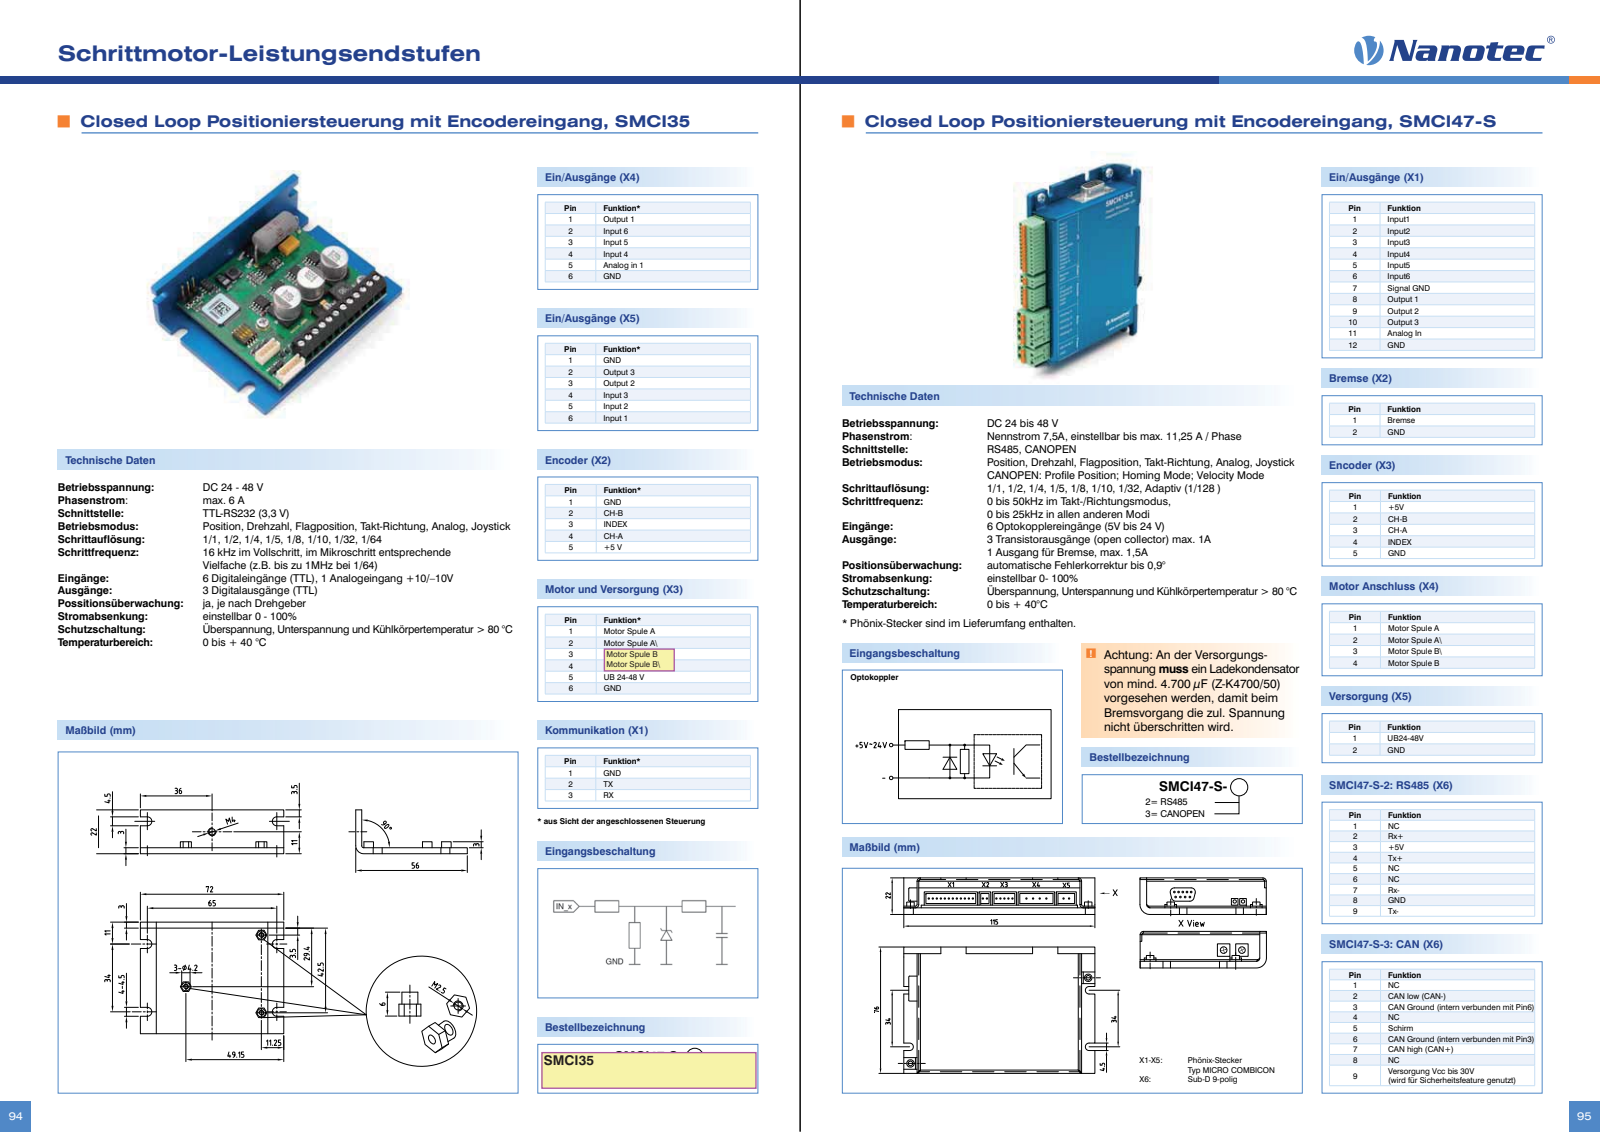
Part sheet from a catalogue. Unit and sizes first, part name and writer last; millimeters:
Units: millimetres
Overall size (bounding box): 115 × 93.3 × 22
Round holes (diameter × count): ⌀1.5 ×19, ⌀1.6 ×16, ⌀1.2 ×9, ⌀1.56 ×9, ⌀1.65 ×9, ⌀2.1 ×9, ⌀4 ×6, ⌀1.4 ×4, ⌀2.8 ×4, ⌀2.16 ×2, ⌀4.15 ×2, ⌀4.3 ×2
Round bosses / shafts (diameter × count): ⌀1.2 ×19, ⌀1.01 ×18, ⌀0.6 ×9, ⌀0.46 ×3, ⌀5.3 ×2, ⌀4 ×2, ⌀2.5 ×2, ⌀2.27 ×2
Partial cylindrical surfaces — rounded edges, fillets, slot ends (radius × count): R0.2 ×52, R0.1 ×39, R0.16 ×30, R2 ×25, R1.3 ×22, R0.3 ×20, R1.5 ×20, R0.55 ×19
Main face-to-face distances: 1, 18, 3, 4.8, 1.8, 17.2, 19, 22, 21, 16.2
Hole centre spacings: 5, 2.5, 1.75, 3.13, 40.8, 38.3, 2.97, 7.5
Volume: 77 264 mm³ · Surface area: 76 686 mm²
Bodies: 16 solids, 4510 faces (3061 planar, 1005 cylindrical, 444 other)
Part name (STEP PRODUCT): SMCI47-S; Ph\S\vnixstecker_FKC2.5HC_4; Ph\S\vnixstecker_FK-MC0.5_2; Ph\S\vnixstecker_FK-MC0.5_5 (+8 more)
STEP written by: Autodesk Inventor 2010 (AUTOMOTIVE_DESIGN)
